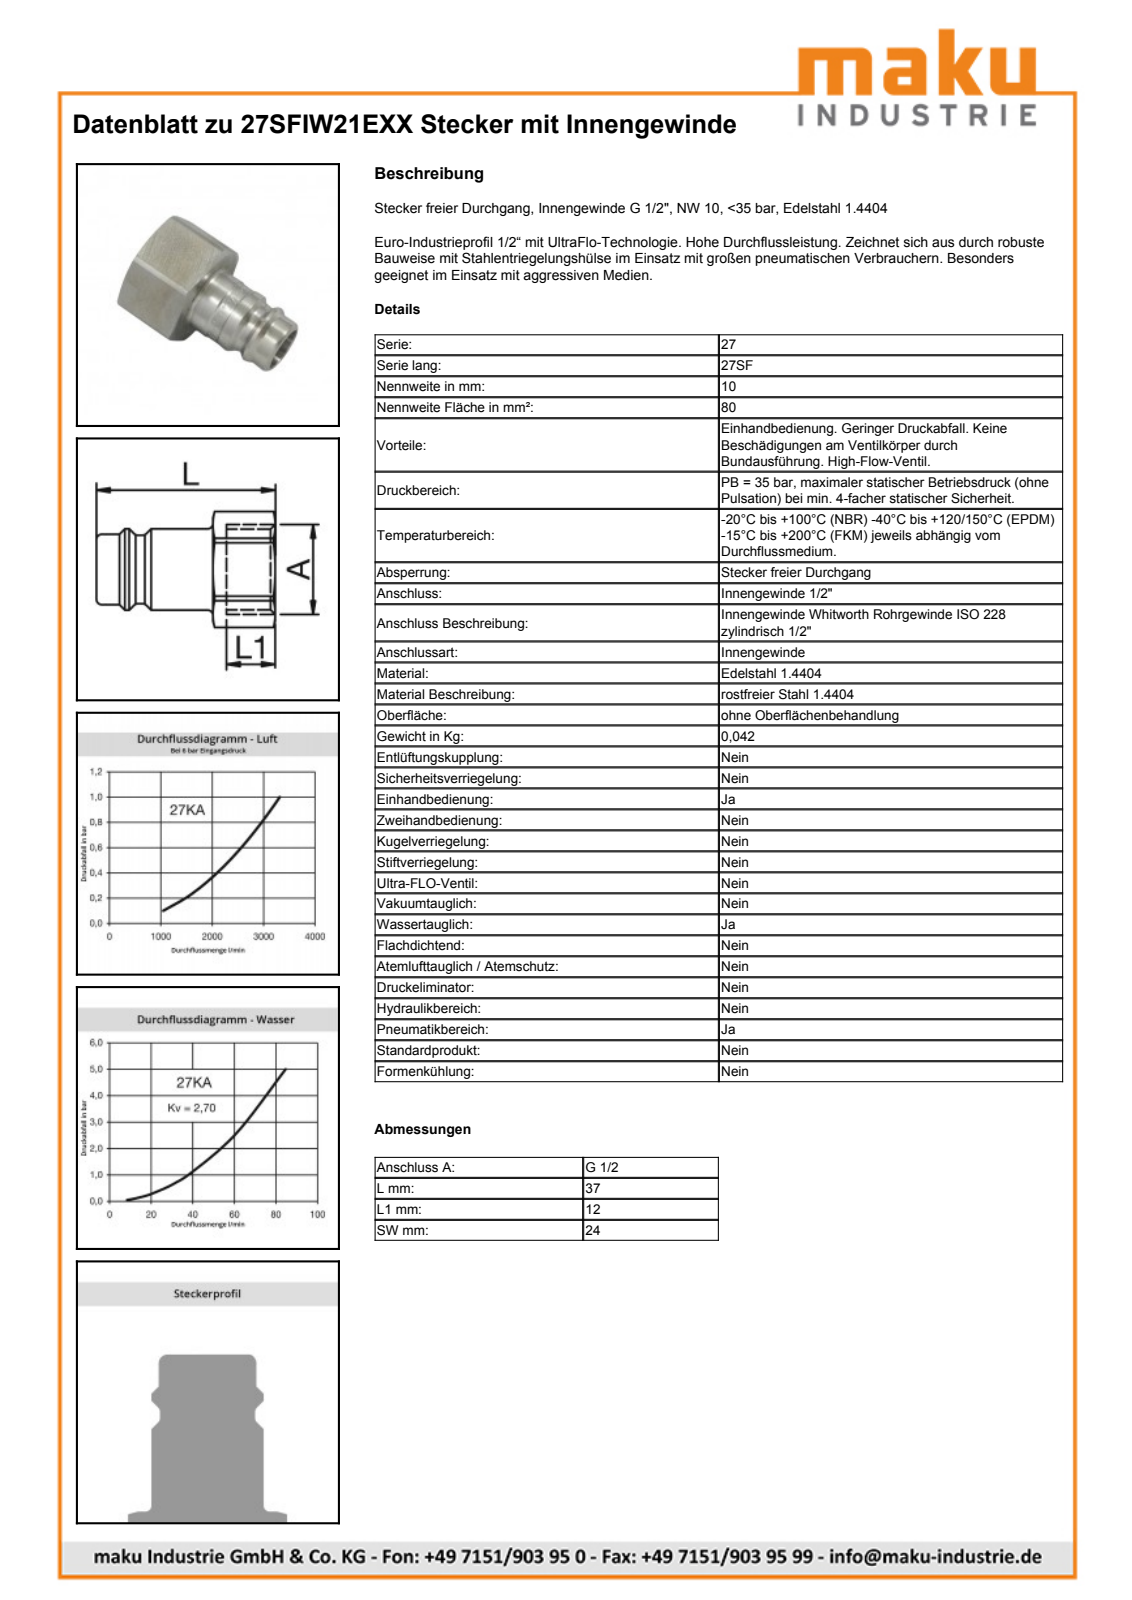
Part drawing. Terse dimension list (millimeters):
name: D106719
written by: Autodesk Inventor 2011 (AUTOMOTIVE_DESIGN)
unit: mm
bodies: 1 solid, 42 faces (10 planar, 12 cylindrical, 20 other)
size: 37 × 27.05 × 24
volume: 4 999 mm³; area: 4 557 mm²
holes: 1× ⌀10, 1× ⌀20.95
bosses: 1× ⌀15, 1× ⌀13, 1× ⌀12.65
rounds: 1× R13.53
face distances: 24, 3.5, 15.5, 12, 21.5, 25, 37
